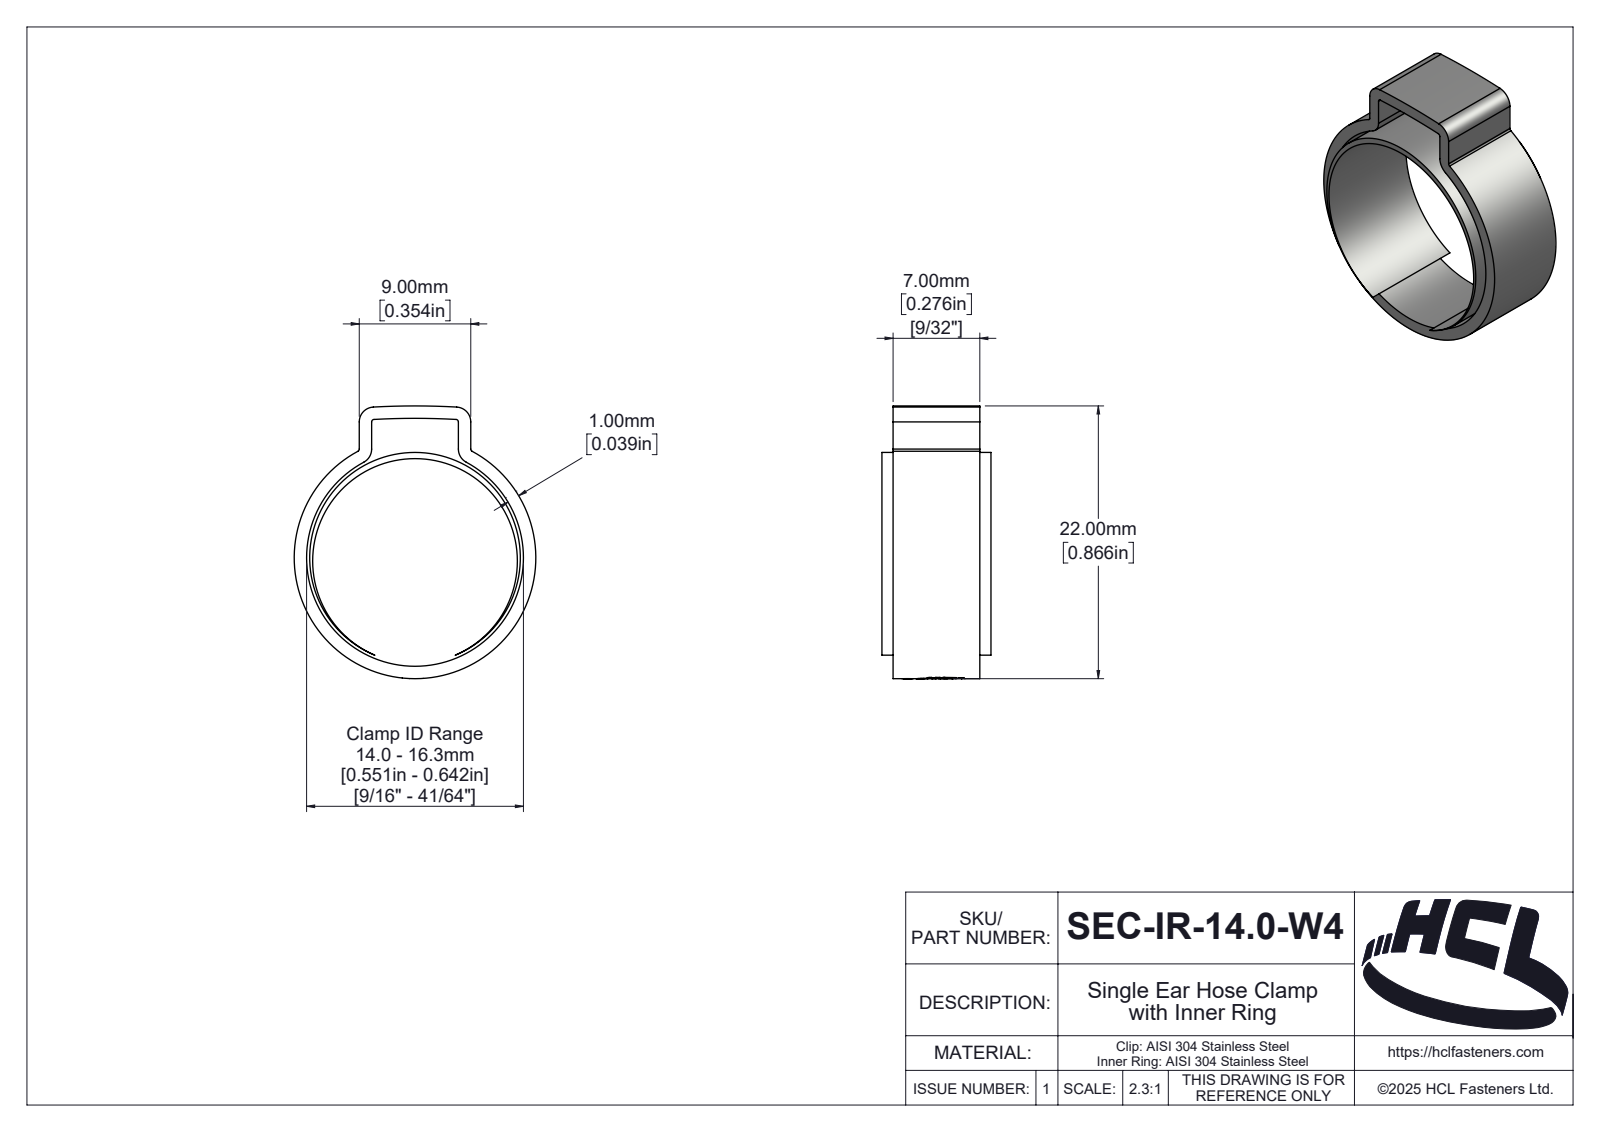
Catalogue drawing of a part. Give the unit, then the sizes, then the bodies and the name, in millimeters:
Units: millimetres
Overall size (bounding box): 22 × 19.5 × 8.8
Round holes (diameter × count): ⌀16.52 ×1, ⌀17.5 ×1
Round bosses / shafts (diameter × count): ⌀19.5 ×1, ⌀17 ×1
Partial cylindrical surfaces — rounded edges, fillets, slot ends (radius × count): R0.2 ×4, R1.2 ×4, R0.21 ×1, R0.88 ×1, R1.09 ×1, R1.15 ×1, R1.39 ×1, R1.97 ×1
Main face-to-face distances: 7, 1, 8, 0.9, 7.9, 9, 8.8, 4.21, 3.21, 3.79
Volume: 557 mm³ · Surface area: 1 858 mm²
Bodies: 2 solids, 131 faces (10 planar, 72 cylindrical, 49 other)
Part name (STEP PRODUCT): SEC-IR-14.0-W4
STEP written by: SolidWorks 2025 (AUTOMOTIVE_DESIGN)
